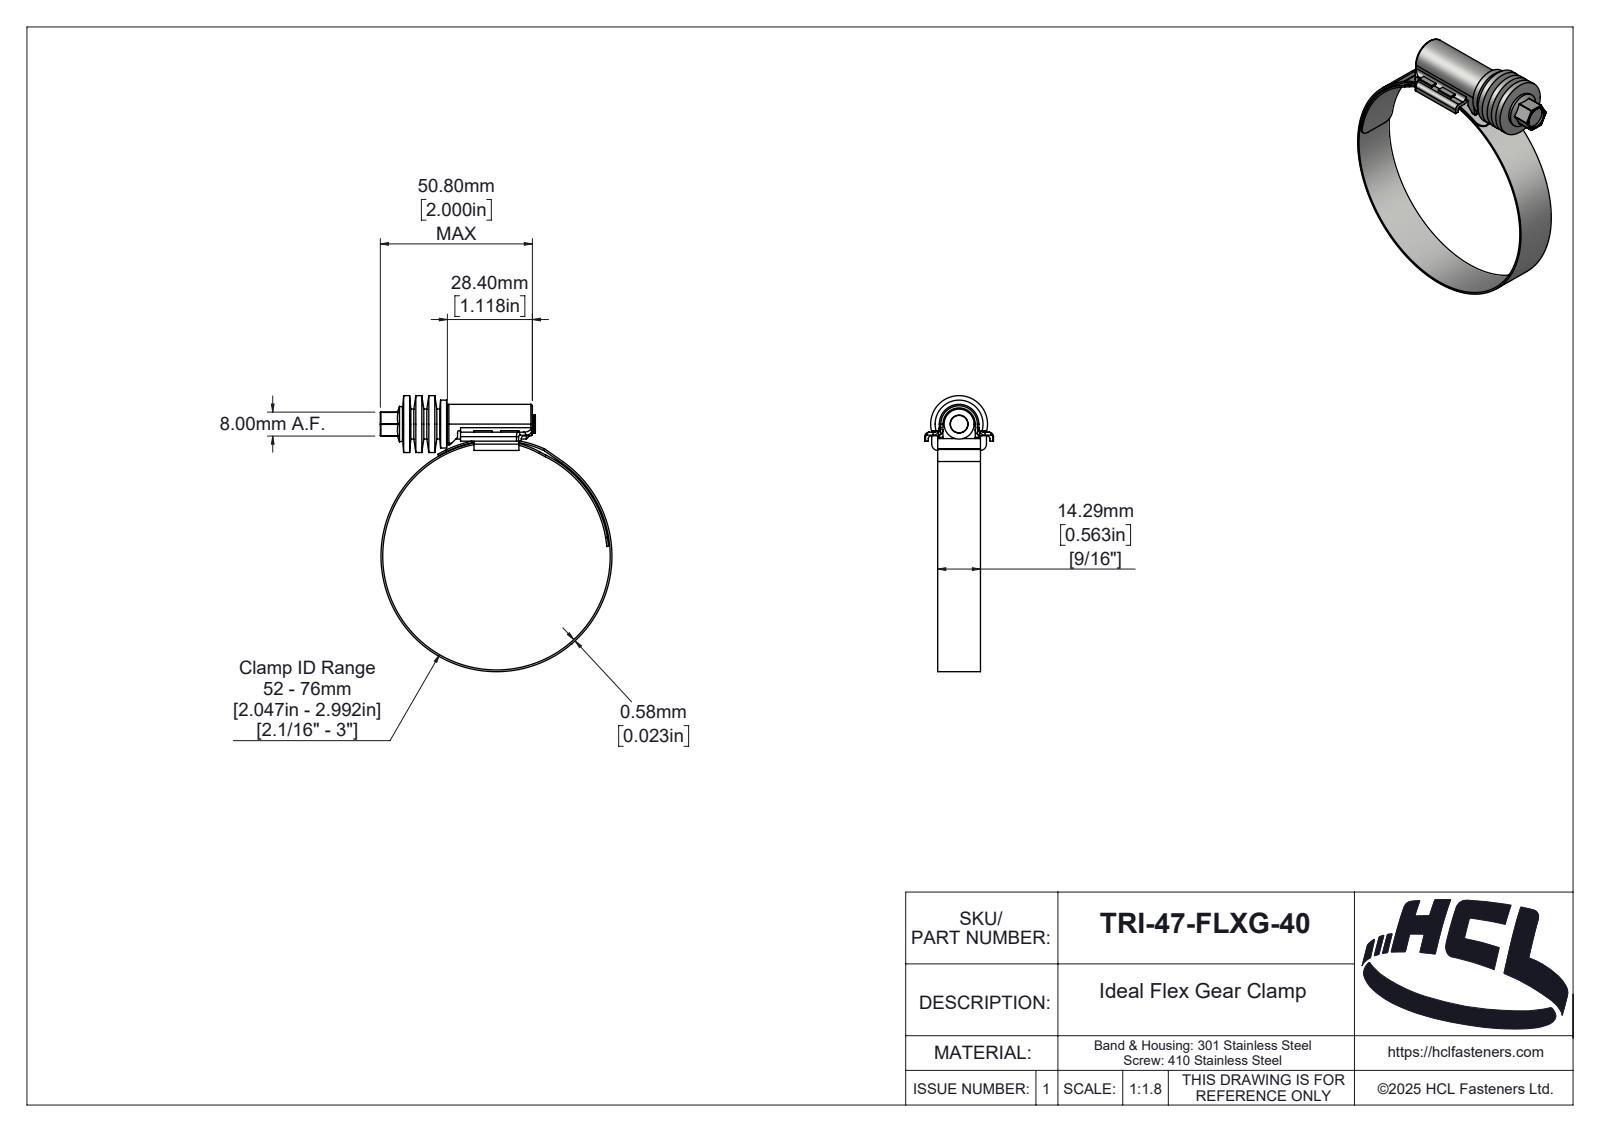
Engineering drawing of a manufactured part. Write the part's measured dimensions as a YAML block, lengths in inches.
part_name: "TRI-47-FLXG-40"
step_written_by: "SolidWorks 2025 (AUTOMOTIVE_DESIGN)"
units: inches
bodies: {solids: 4, faces: 323, planar: 88, cylindrical: 139, other: 96}
overall_size: [3.629, 3.046, 0.906]
volume: 0.623
surface_area: 24.61
round_holes:
  - {diameter: 0.276, count: 1}
  - {diameter: 2.992, count: 1}
round_bosses_or_shafts:
  - {diameter: 3.038, count: 1}
  - {diameter: 0.748, count: 1}
  - {diameter: 0.63, count: 1}
  - {diameter: 0.394, count: 1}
  - {diameter: 0.236, count: 1}
  - {diameter: 0.197, count: 1}
partial_cylinders:
  - {radius: 0.008, count: 12}
  - {radius: 0.02, count: 9}
  - {radius: 0.039, count: 8}
  - {radius: 0.059, count: 4}
  - {radius: 0.118, count: 4}
  - {radius: 0.079, count: 3}
  - {radius: 0.004, count: 2}
  - {radius: 0.083, count: 2}
face_to_face_distances: [0.079, 0.562, 0.047, 0.193, 0.069, 0.494, 0.641, 0.24, 0.023, 0.021]
